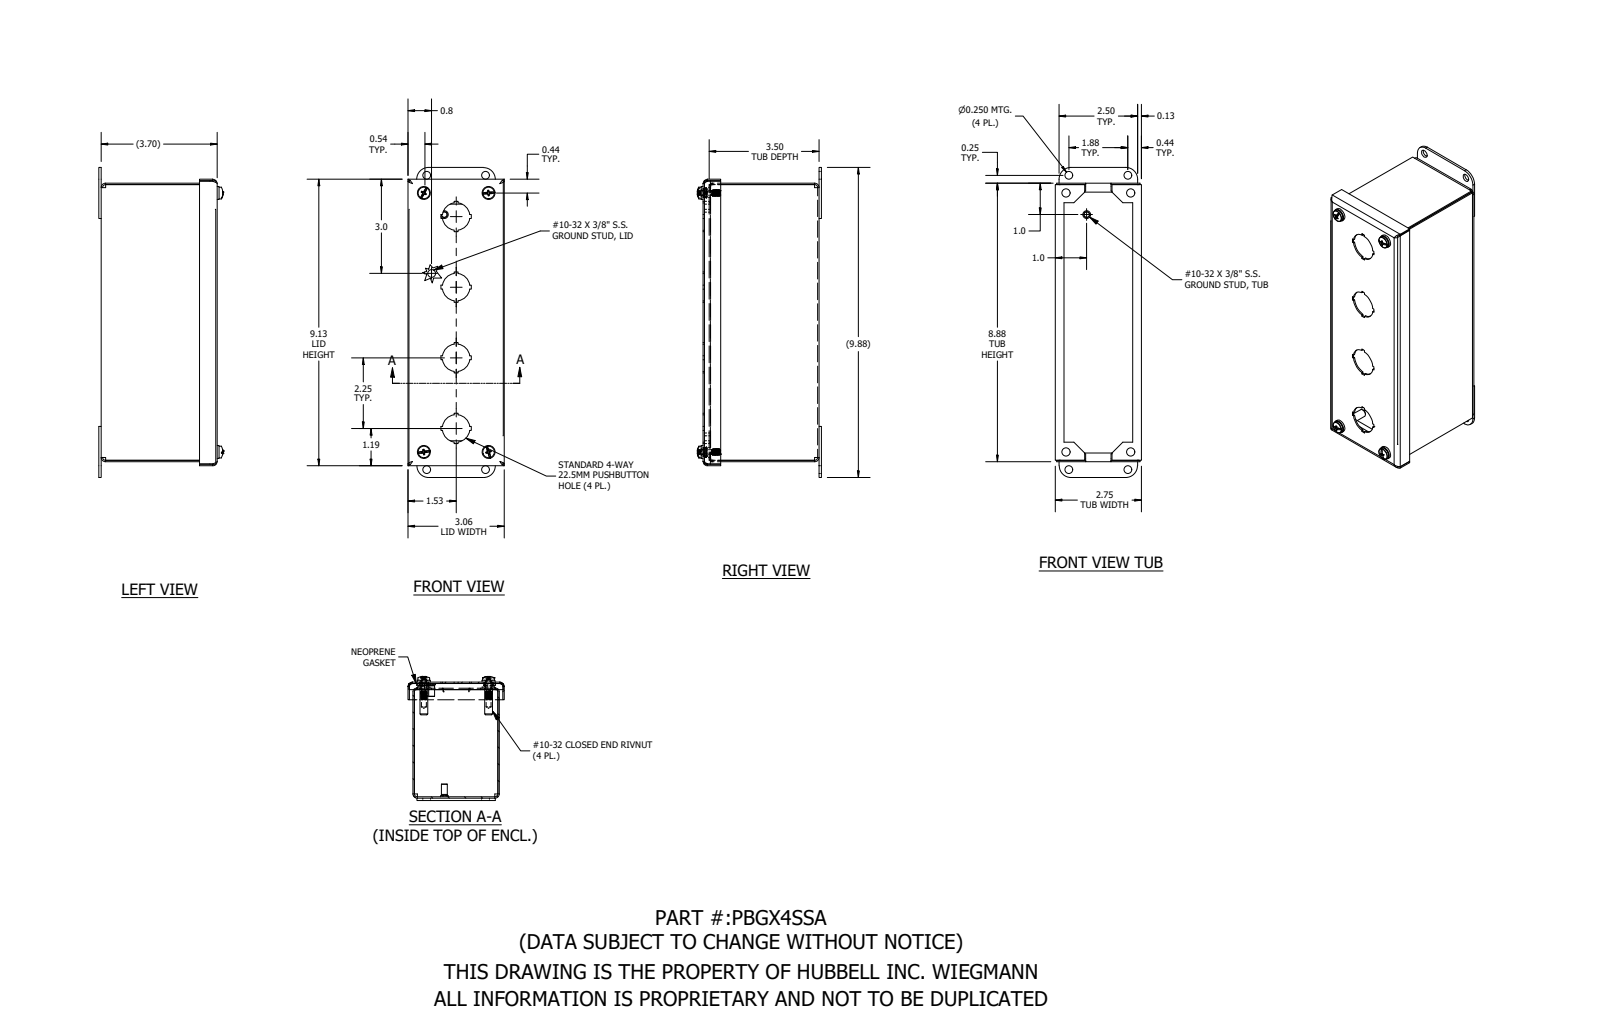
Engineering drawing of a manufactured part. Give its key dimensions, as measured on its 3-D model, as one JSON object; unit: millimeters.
{"part_name": "PBGX4SSA", "step_written_by": "SolidWorks 2021 (AUTOMOTIVE_DESIGN)", "units": "millimeters", "bodies": {"solids": 20, "faces": 776, "planar": 364, "cylindrical": 260, "other": 152}, "overall_size": [250.8, 100.4, 77.8], "volume_mm3": 156100, "surface_area_mm2": 227500, "round_holes": [[4, 4], [5, 4], [6.4, 4], [6.5, 4], [7.1, 4], [8, 4], [22.2, 4], [3.4, 2], [4.4, 2], [4.4, 2]], "round_bosses_or_shafts": [[10.3, 4], [8.1, 4], [6.3, 4], [4.7, 4], [3.6, 4], [3.6, 4], [9.5, 3], [6.4, 2]], "partial_cylinders_radius": [[2.4, 8], [3.5, 8], [1.6, 4], [2.7, 4], [9.5, 4]], "face_to_face_distances": [1.1, 1.1, 92.7, 68.7, 69.9, 67.6, 68.7, 93.9, 91.6, 4], "hole_center_spacings": [32.4, 80.6, 135.9, 149.6, 192.3, 206.2, 223.9, 229.4]}
